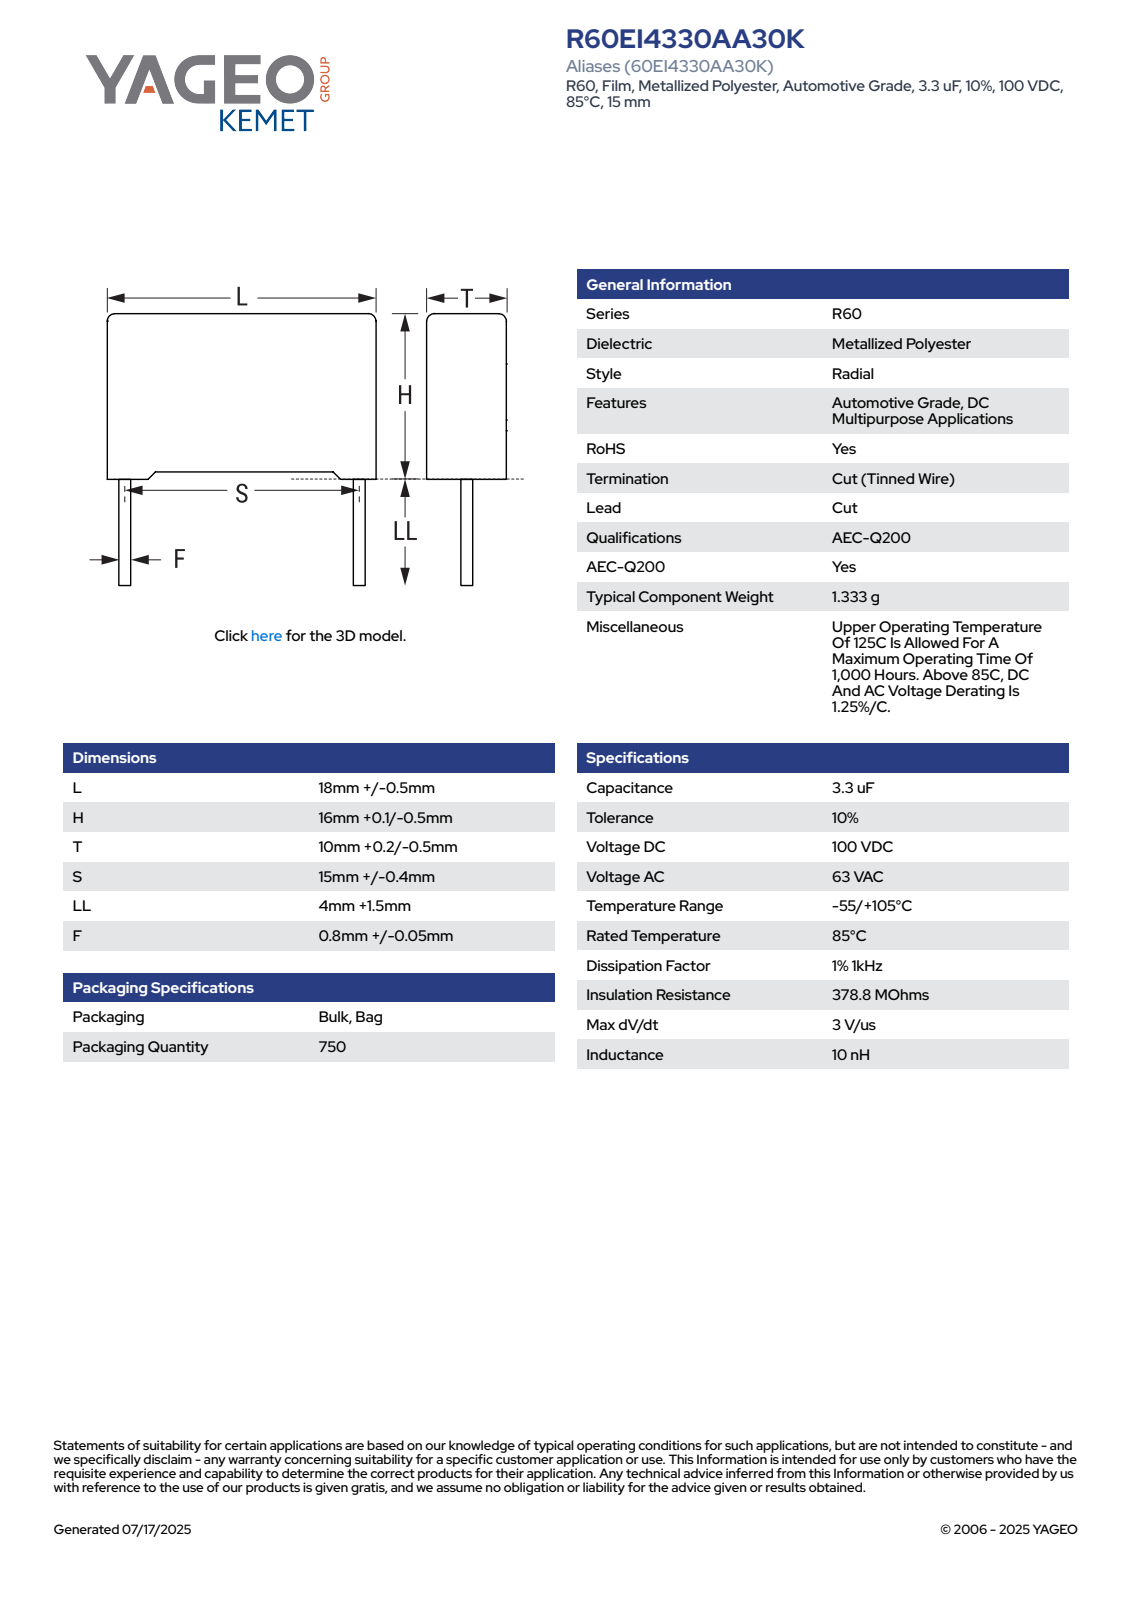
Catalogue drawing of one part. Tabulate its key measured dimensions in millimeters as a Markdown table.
| quantity | value |
| --- | --- |
| part name | CFR_RB2_18X16X10_L18.5H16.1T10.2S15LL5.5F0.85 |
| STEP written by | SolidWorks 2021 (AUTOMOTIVE_DESIGN) |
| units | millimeters |
| bodies | 4 solids, 85 faces (77 planar, 8 cylindrical, 0 other) |
| overall size | 21.6 × 18.5 × 10.21 |
| volume | 2 918 mm³ |
| surface area | 1 363 mm² |
| round bosses / shafts (diameter × count) | 0.85 × 2 |
| partial cylindrical surfaces (radius × count) | 0.5 × 4 |
| main face-to-face distances | 10.2, 18.5, 15.35, 0.62, 0.75, 16.1, 0.56, 15.54, 17.88, 9.58 |
